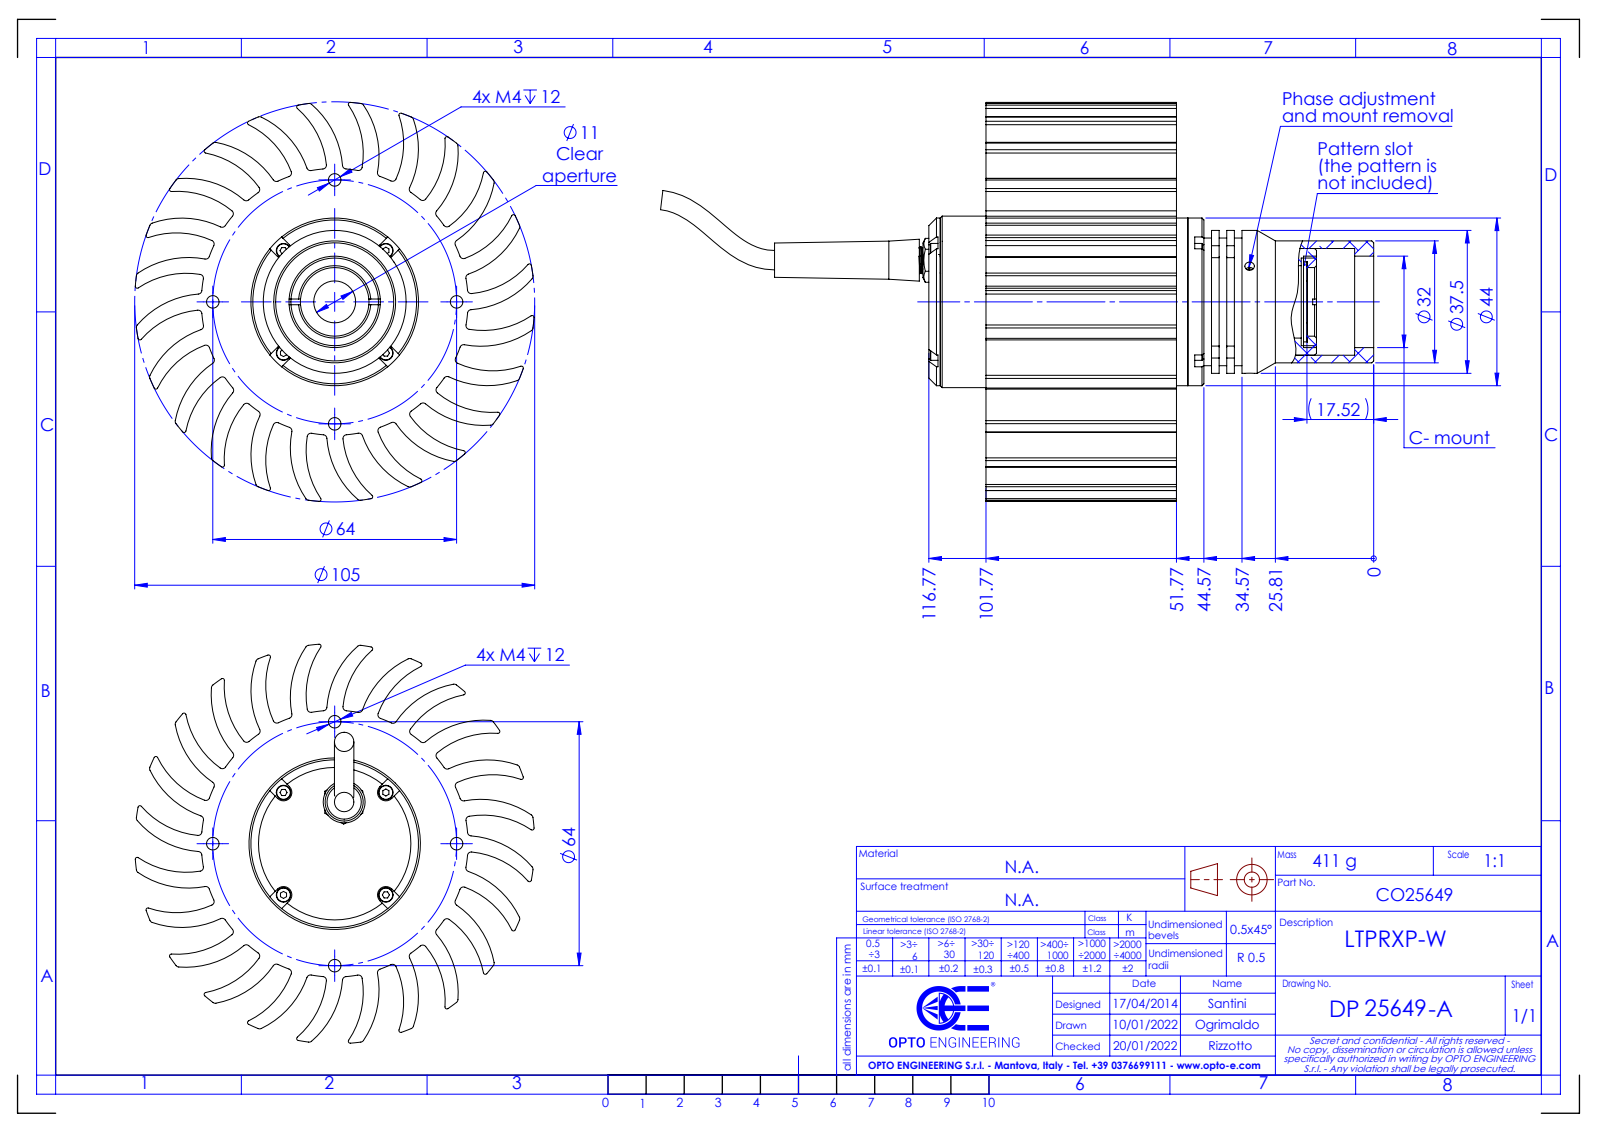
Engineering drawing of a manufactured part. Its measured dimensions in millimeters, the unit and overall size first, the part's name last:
Units: millimetres
Overall size (bounding box): 187.2 × 104.68 × 104.68
Round holes (diameter × count): ⌀3.3 ×4, ⌀2.5 ×3, ⌀24 ×1, ⌀28 ×1
Round bosses / shafts (diameter × count): ⌀3.8 ×4, ⌀45 ×1, ⌀44 ×1, ⌀37.5 ×1, ⌀33.5 ×1, ⌀32 ×1
Partial cylindrical surfaces — rounded edges, fillets, slot ends (radius × count): R1 ×72, R0.5 ×24, R22.57 ×24, R23.5 ×24, R2.2 ×4, R2.25 ×4, R35 ×1, R52.5 ×1
Main face-to-face distances: 50, 65, 3, 15, 68, 53, 2, 12, 62, 4
Hole centre spacings: 32, 45.25, 64
Bodies: 0 solids, 473 faces (101 planar, 314 cylindrical, 58 other)
Part name (STEP PRODUCT): DP25649-A_LTPRXP-W
STEP written by: SolidWorks 2021 (CONFIG_CONTROL_DESIGN)
